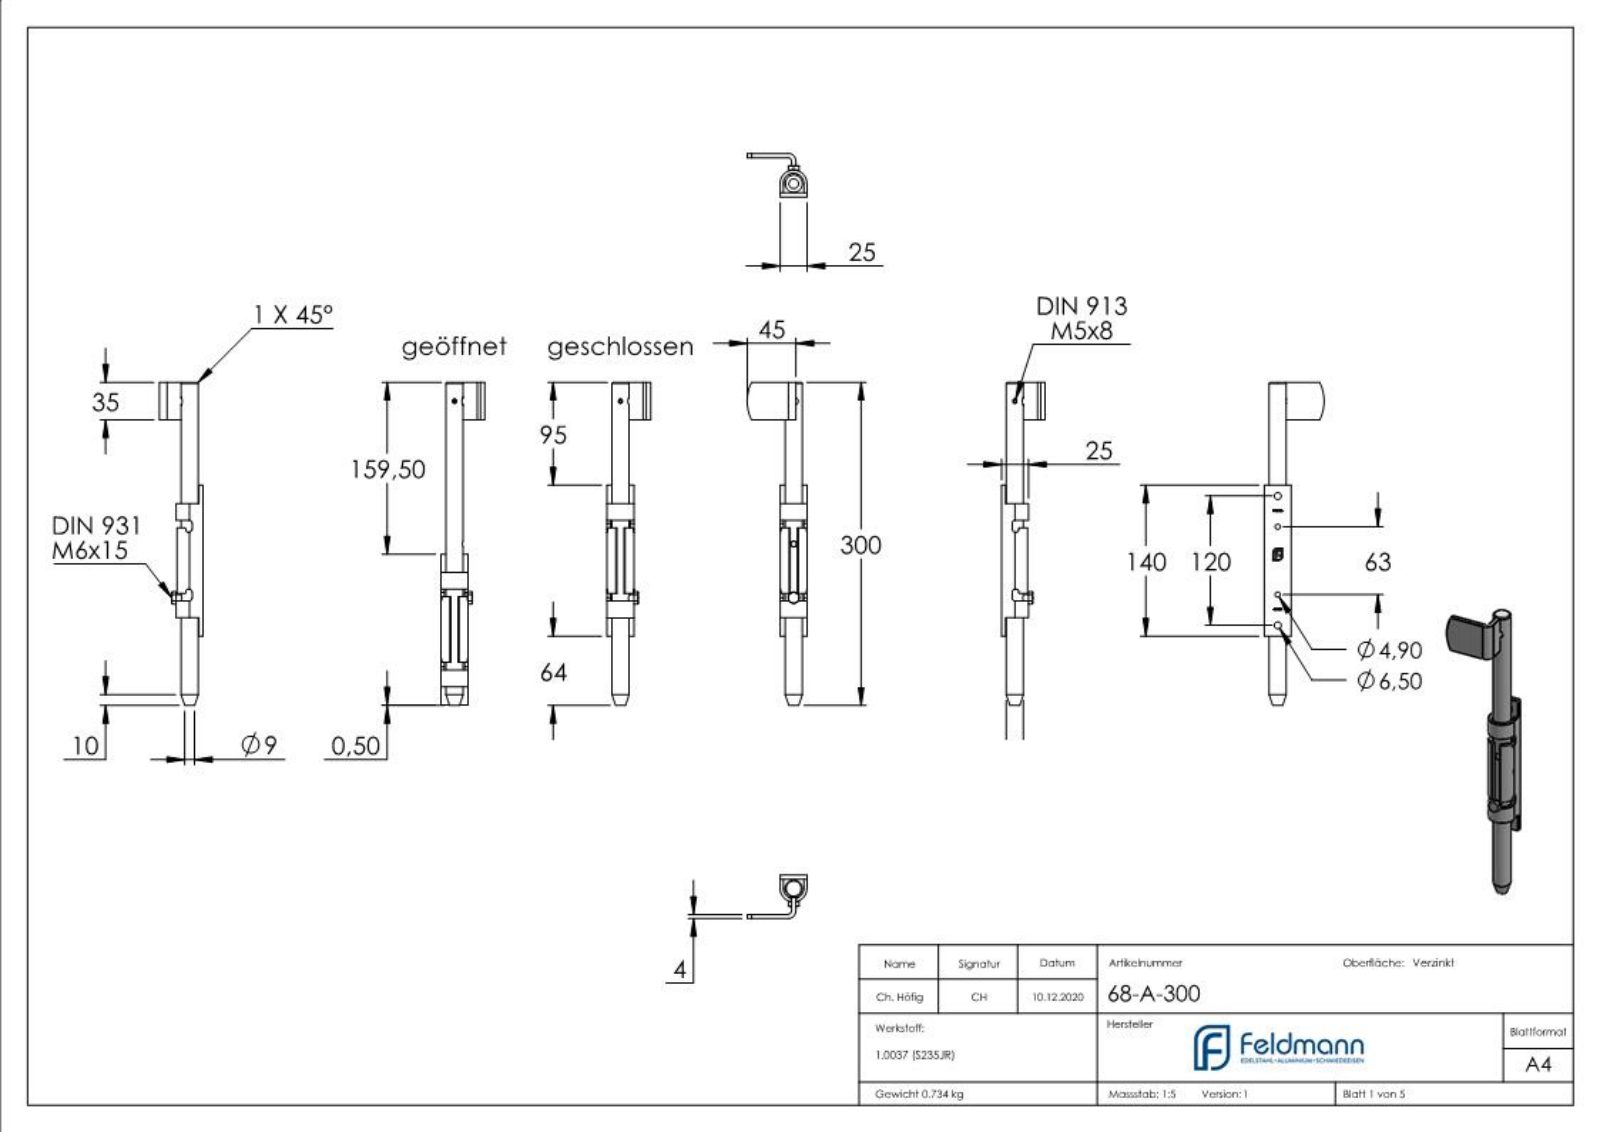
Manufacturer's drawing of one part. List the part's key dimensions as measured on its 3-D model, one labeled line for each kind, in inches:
Part name (STEP PRODUCT): 68-A-300; DIN913_DIN 913 M6x10; 68-A-X00 Teil3_68-A-X00 Teil3; DIN 931_DIN 931 M6x20 (+2 more)
STEP written by: SolidWorks 2018 (CONFIG_CONTROL_DESIGN)
Units: inches
Bodies: 5 solids, 380 faces (190 planar, 43 cylindrical, 147 other)
Overall size (bounding box): 11.811 × 1.841 × 1.506
Volume: 5.544 in³ · Surface area: 58.21 in²
Round holes (diameter × count): ⌀0.197 ×3, ⌀0.217 ×2, ⌀0.335 ×2, ⌀0.02 ×1, ⌀0.295 ×1
Round bosses / shafts (diameter × count): ⌀0.236 ×2, ⌀0.63 ×1
Partial cylindrical surfaces — rounded edges, fillets, slot ends (radius × count): R0.039 ×6, R0.118 ×4, R0.079 ×3, R0.236 ×1, R0.344 ×1, R0.463 ×1, R1.575 ×1
Main face-to-face distances: 0.157, 1.348, 0.118, 0.807, 0.925, 1.506, 1.191, 0.541, 0.266, 0.423
Hole centre spacings: 1.043, 3.563, 0.02, 0.059, 0.984, 1.063, 2.5, 2.52
